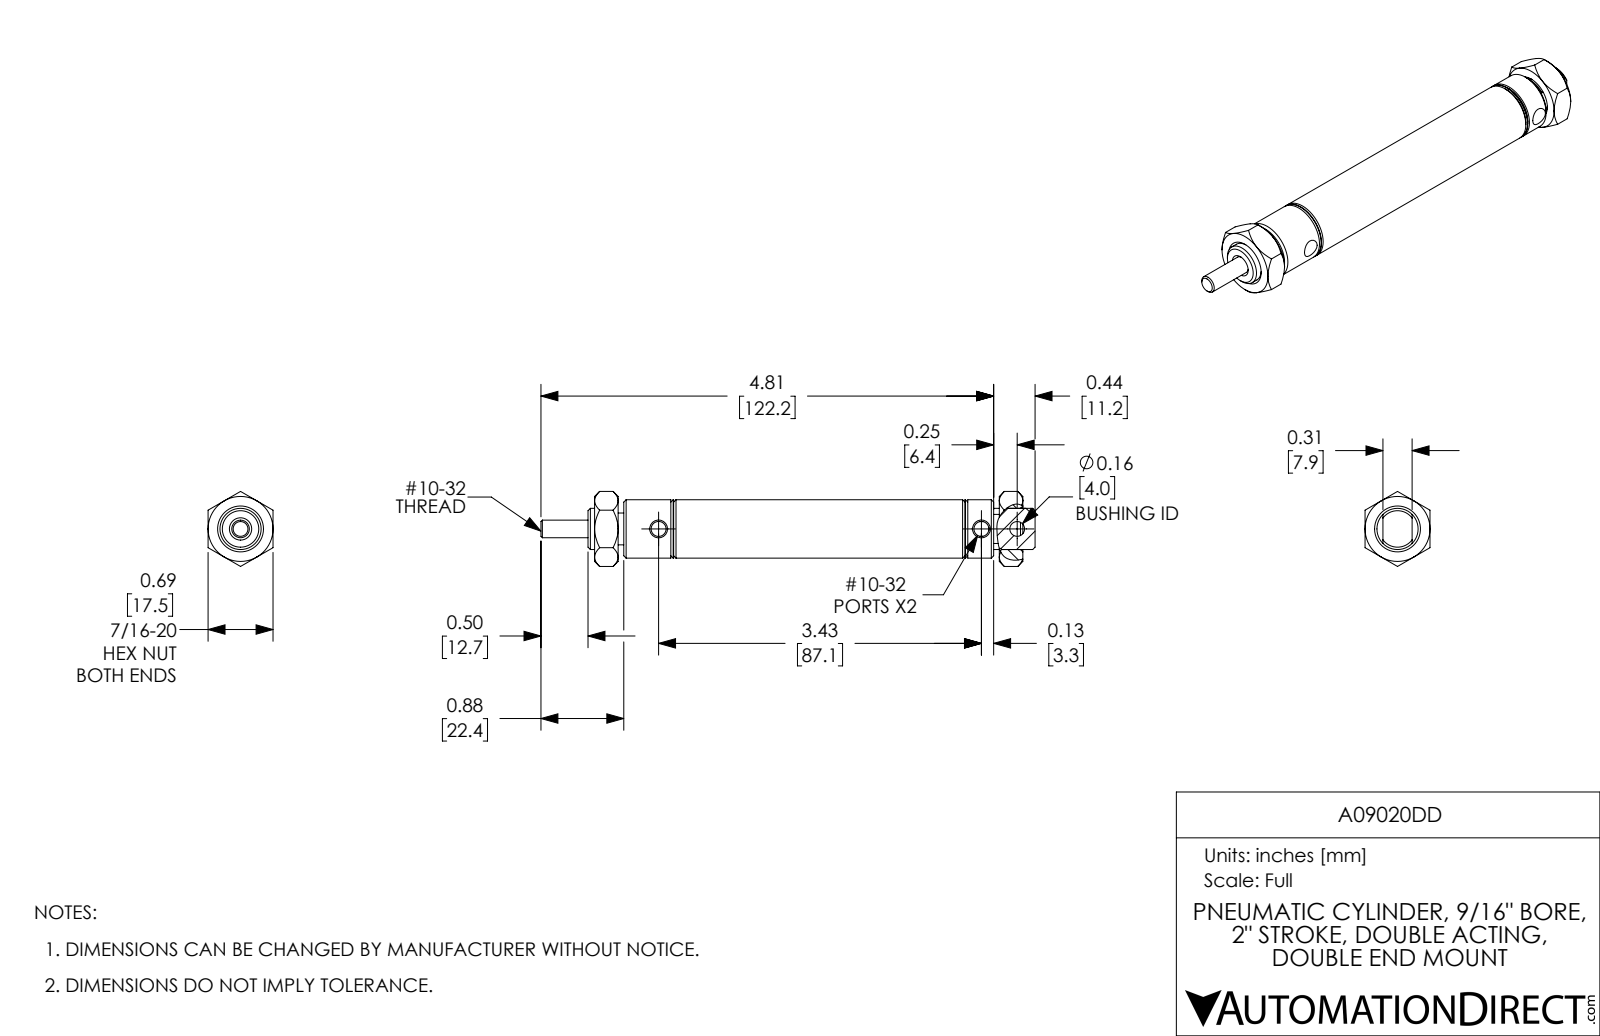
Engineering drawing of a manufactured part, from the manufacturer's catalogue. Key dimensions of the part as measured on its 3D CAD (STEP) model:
Part name (STEP PRODUCT): A09020DD-MainBody; A09020DD; A09020DD_Mounting Nut_D-154; A09020DD-Rod
STEP written by: SolidWorks 2017 (AUTOMOTIVE_DESIGN)
Units: inches
Bodies: 4 solids, 151 faces (36 planar, 46 cylindrical, 69 other)
Overall size (bounding box): 5.25 × 0.797 × 0.69
Volume: 0.957 in³ · Surface area: 21.94 in²
Round holes (diameter × count): ⌀0.159 ×2, ⌀0.19 ×2, ⌀0.156 ×1, ⌀0.157 ×1, ⌀0.187 ×1, ⌀0.563 ×1
Round bosses / shafts (diameter × count): ⌀0.62 ×1, ⌀0.437 ×1, ⌀0.338 ×1
Main face-to-face distances: 0.69, 0.5, 0.25, 4.3, 0.715, 3.215, 3.275, 0.31, 2.5, 0.775
Hole centre spacings: 0.38, 3.43, 3.81
